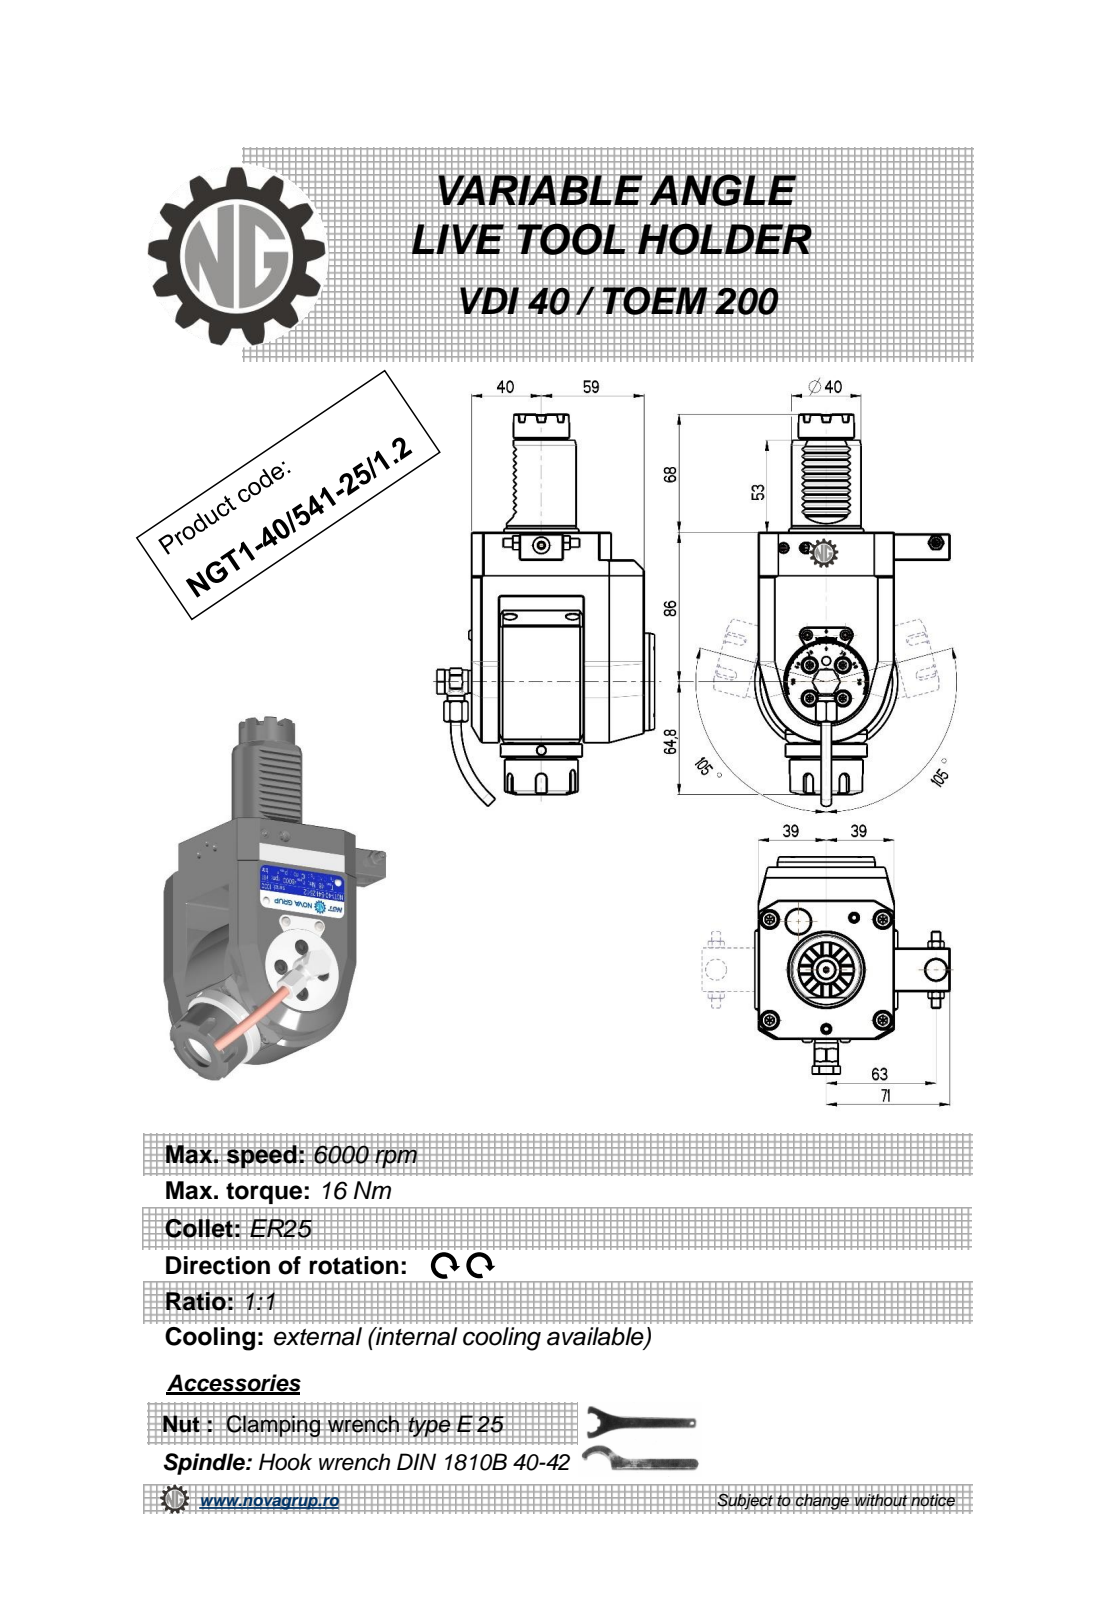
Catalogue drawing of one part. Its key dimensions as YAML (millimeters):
part_name: "NGT1_40_541_25_1_2"
step_written_by: "PRO/ENGINEER BY PARAMETRIC TECHNOLOGY CORPORATION, 2010280 (CONFIG_CONTROL_DESIGN)"
units: millimeters
bodies: {solids: 1, faces: 645, planar: 272, cylindrical: 142, other: 231}
overall_size: [225.67, 124.9, 112]
volume: 917488
surface_area: 85357
round_holes:
  - {diameter: 4, count: 3}
  - {diameter: 5, count: 2}
  - {diameter: 3, count: 1}
  - {diameter: 4.2, count: 1}
  - {diameter: 4.5, count: 1}
  - {diameter: 6.2, count: 1}
  - {diameter: 9, count: 1}
  - {diameter: 9.5, count: 1}
  - {diameter: 11, count: 1}
  - {diameter: 12, count: 1}
  - {diameter: 20.3, count: 1}
round_bosses_or_shafts:
  - {diameter: 10, count: 2}
  - {diameter: 6, count: 2}
  - {diameter: 5.7, count: 2}
  - {diameter: 82, count: 1}
  - {diameter: 56, count: 1}
  - {diameter: 47, count: 1}
  - {diameter: 42, count: 1}
  - {diameter: 40, count: 1}
partial_cylinders:
  - {radius: 0.26, count: 12}
  - {radius: 0.3, count: 10}
  - {radius: 3, count: 5}
  - {radius: 0.5, count: 4}
  - {radius: 1, count: 2}
  - {radius: 10, count: 2}
  - {radius: 7.7, count: 1}
  - {radius: 8.6, count: 1}
face_to_face_distances: [16, 37, 78, 99, 64, 105, 6, 21, 89, 83]
hole_center_spacings: [0.4, 39.45, 49, 49.4, 63, 79.81, 80.06, 101.83]
